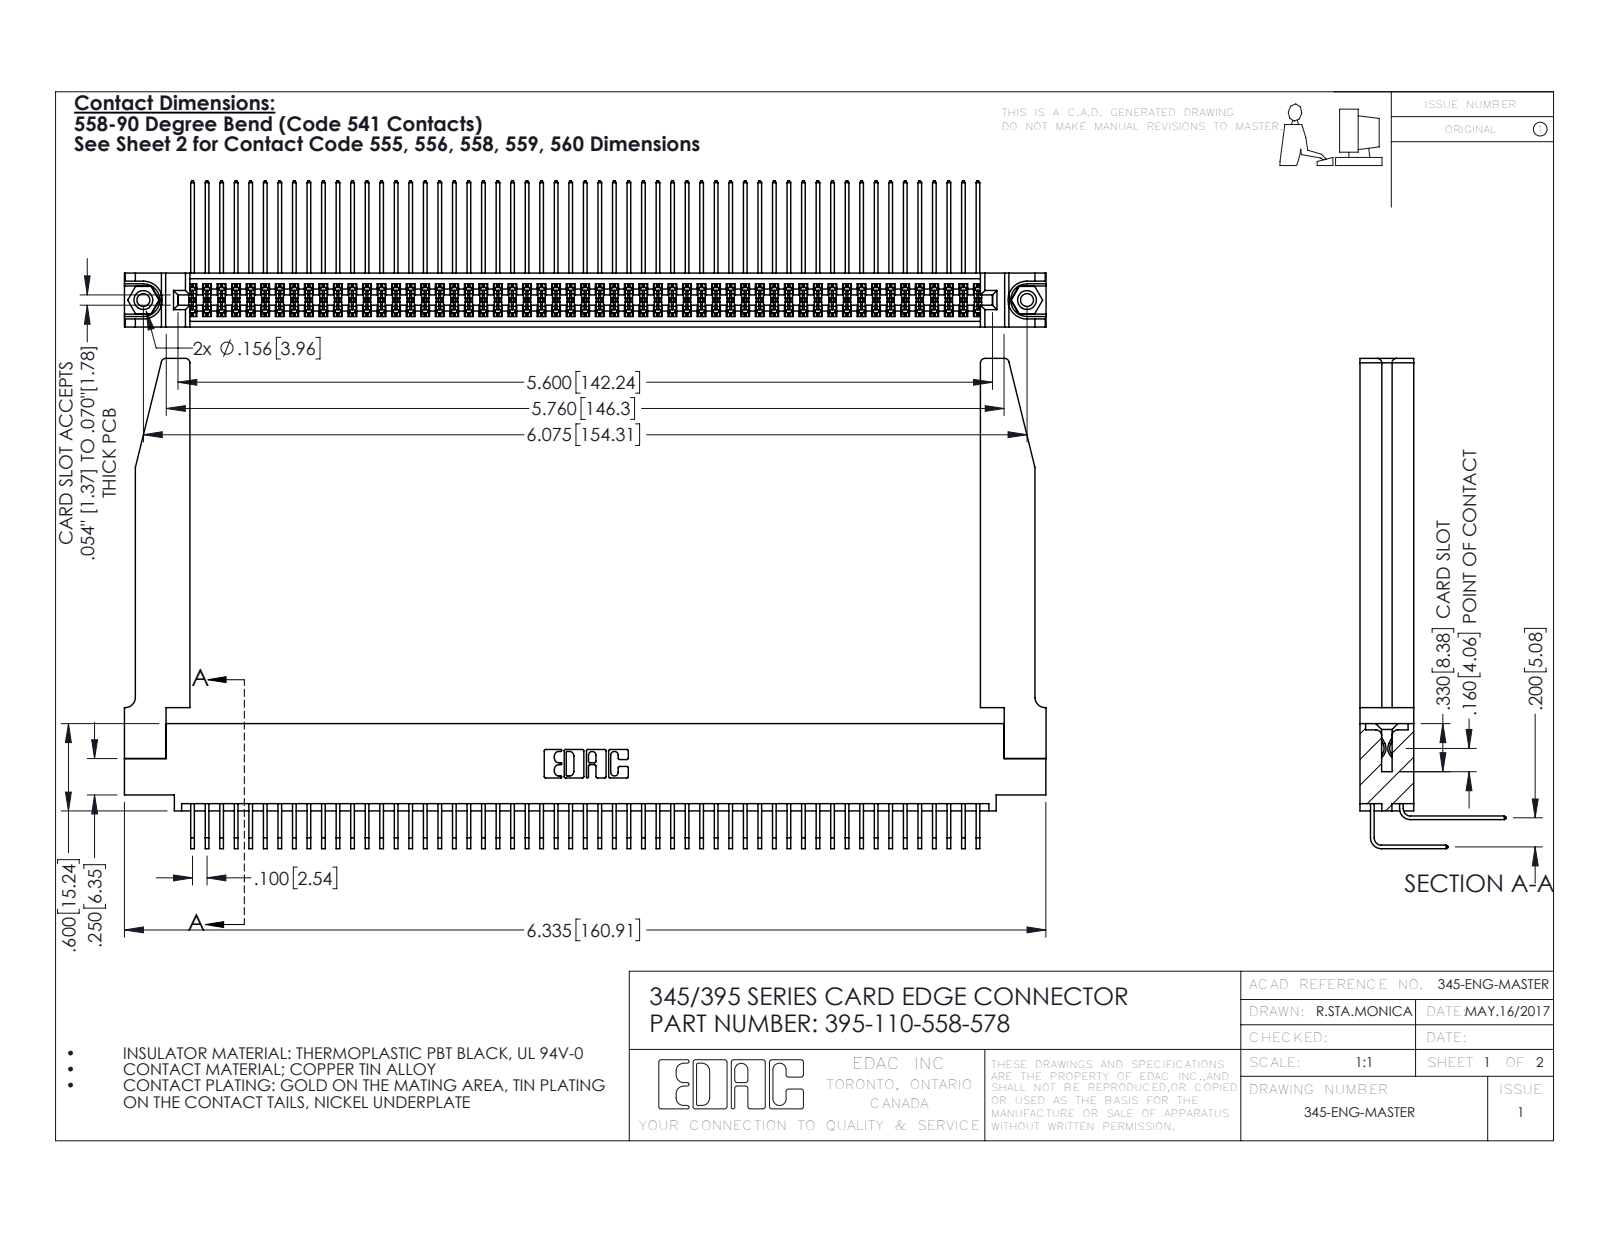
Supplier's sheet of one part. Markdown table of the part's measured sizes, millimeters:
| quantity | value |
| --- | --- |
| part name | 345-220-078_345-220-078; 395-110-558-578; 345-292-001_558 Tail - 2; 345-292-001_558 559 Tail - 1 (+2 more) |
| STEP written by | SolidWorks 2016 (CONFIG_CONTROL_DESIGN) |
| units | millimeters |
| bodies | 115 solids, 6084 faces (4076 planar, 1956 cylindrical, 52 other) |
| overall size | 160.9 × 85.6 × 25.5 |
| volume | 24 090 mm³ |
| surface area | 34 280 mm² |
| round holes (diameter × count) | 2.3 × 2, 3.2 × 2, 4 × 2, 1.6 × 1 |
| round bosses / shafts (diameter × count) | 3.9 × 2 |
| partial cylindrical surfaces (radius × count) | 0.2 × 165, 0.3 × 22, 0.8 × 8, 0.2 × 6, 0.8 × 6, 0.7 × 3, 0.4 × 2, 0.5 × 2 |
| main face-to-face distances | 1.8, 7.6, 9.4, 5.1, 2.5, 6.9, 0.6, 5.7, 0.6, 4.4 |
| hole center spacings | 6.9, 148.3, 154.3 |
